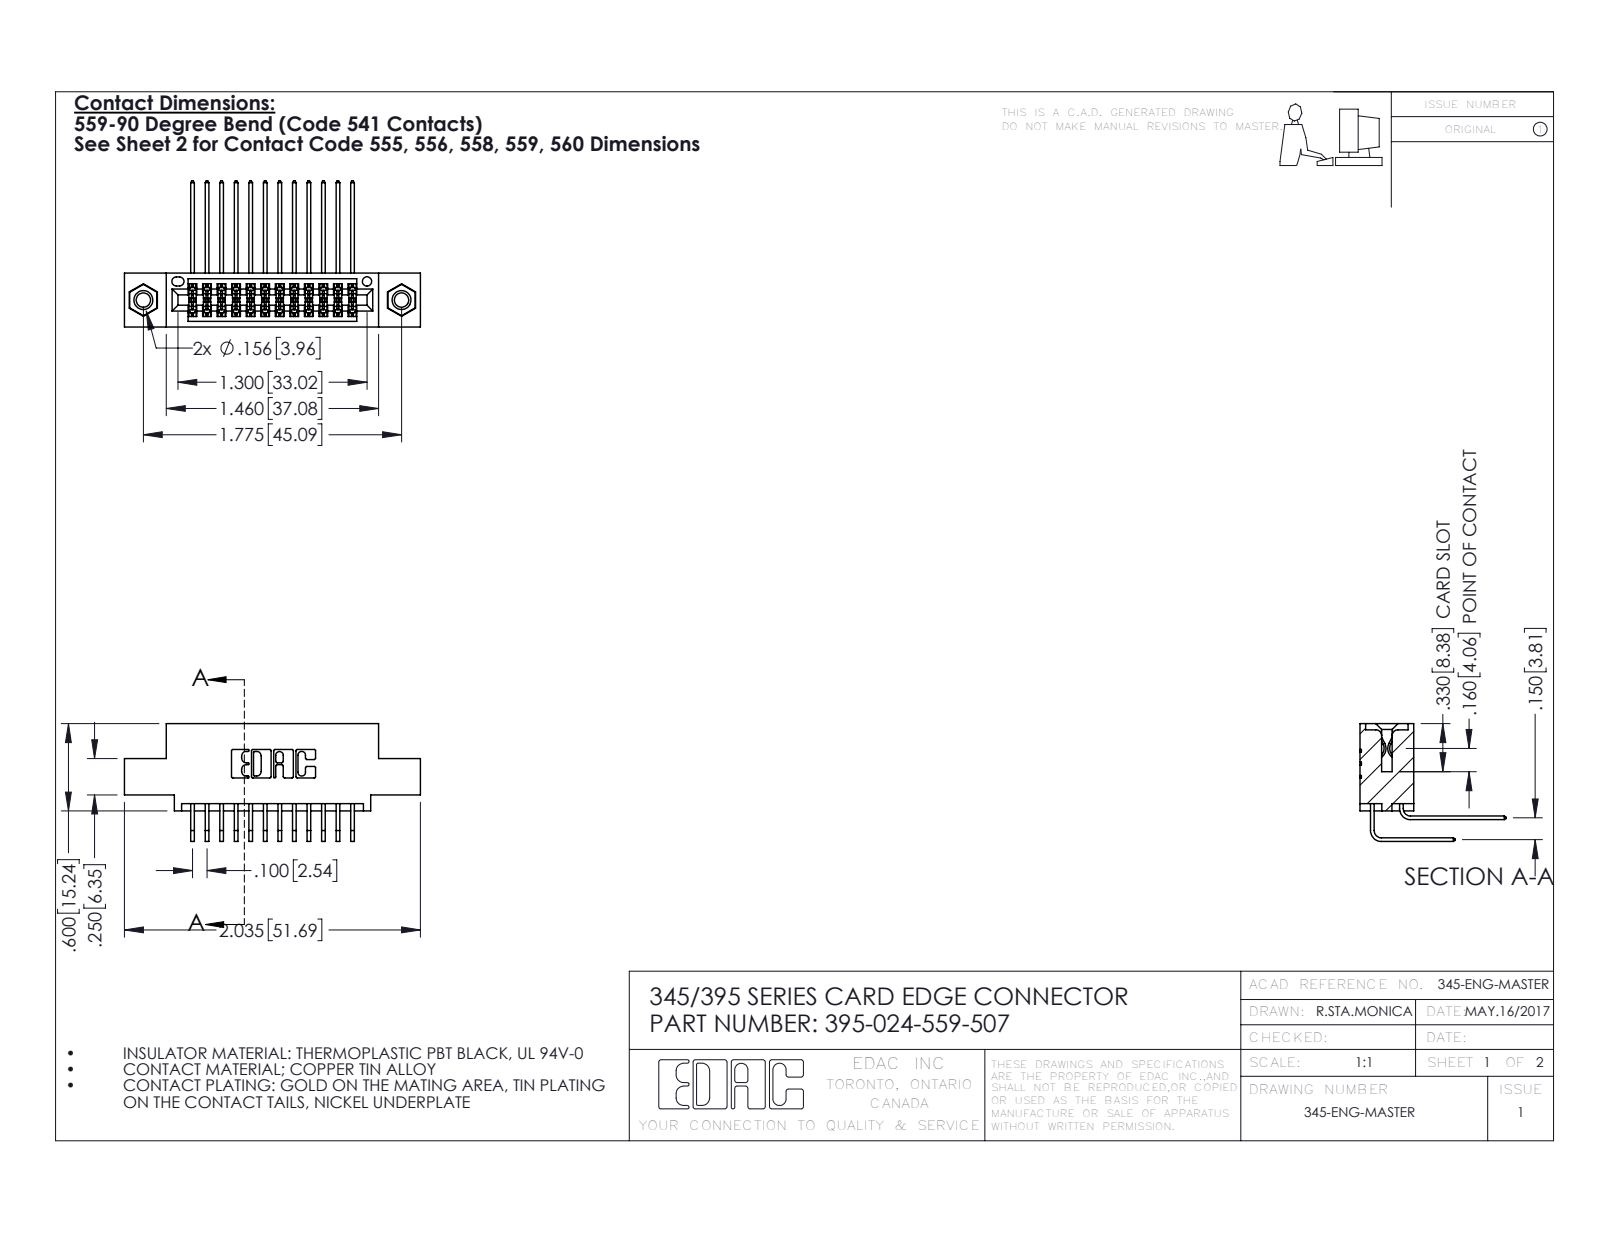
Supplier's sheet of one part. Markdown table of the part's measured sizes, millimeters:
| quantity | value |
| --- | --- |
| part name | 345-292-001_559 Tail - 2; 395-024-559-507; 345 Part_0.110 Offset - 0.156 Dia-TI; 345-250-001_345-250-005-103 (+1 more) |
| STEP written by | SolidWorks 2016 (CONFIG_CONTROL_DESIGN) |
| units | millimeters |
| bodies | 27 solids, 1438 faces (956 planar, 466 cylindrical, 16 other) |
| overall size | 51.7 × 25.5 × 20.5 |
| volume | 4 800 mm³ |
| surface area | 7 277 mm² |
| round holes (diameter × count) | 2.5 × 2, 3.2 × 2, 4 × 2, 1.6 × 1 |
| round bosses / shafts (diameter × count) | 3.9 × 2 |
| partial cylindrical surfaces (radius × count) | 0.2 × 37, 0.3 × 22, 0.2 × 6, 0.8 × 6, 0.7 × 3, 0.4 × 2, 0.5 × 2, 0.6 × 2 |
| main face-to-face distances | 1.8, 7.6, 5.1, 9.4, 2.5, 6.9, 0.6, 5.7, 3.8, 2.5 |
| hole center spacings | 6.9, 39.2, 45.1 |
